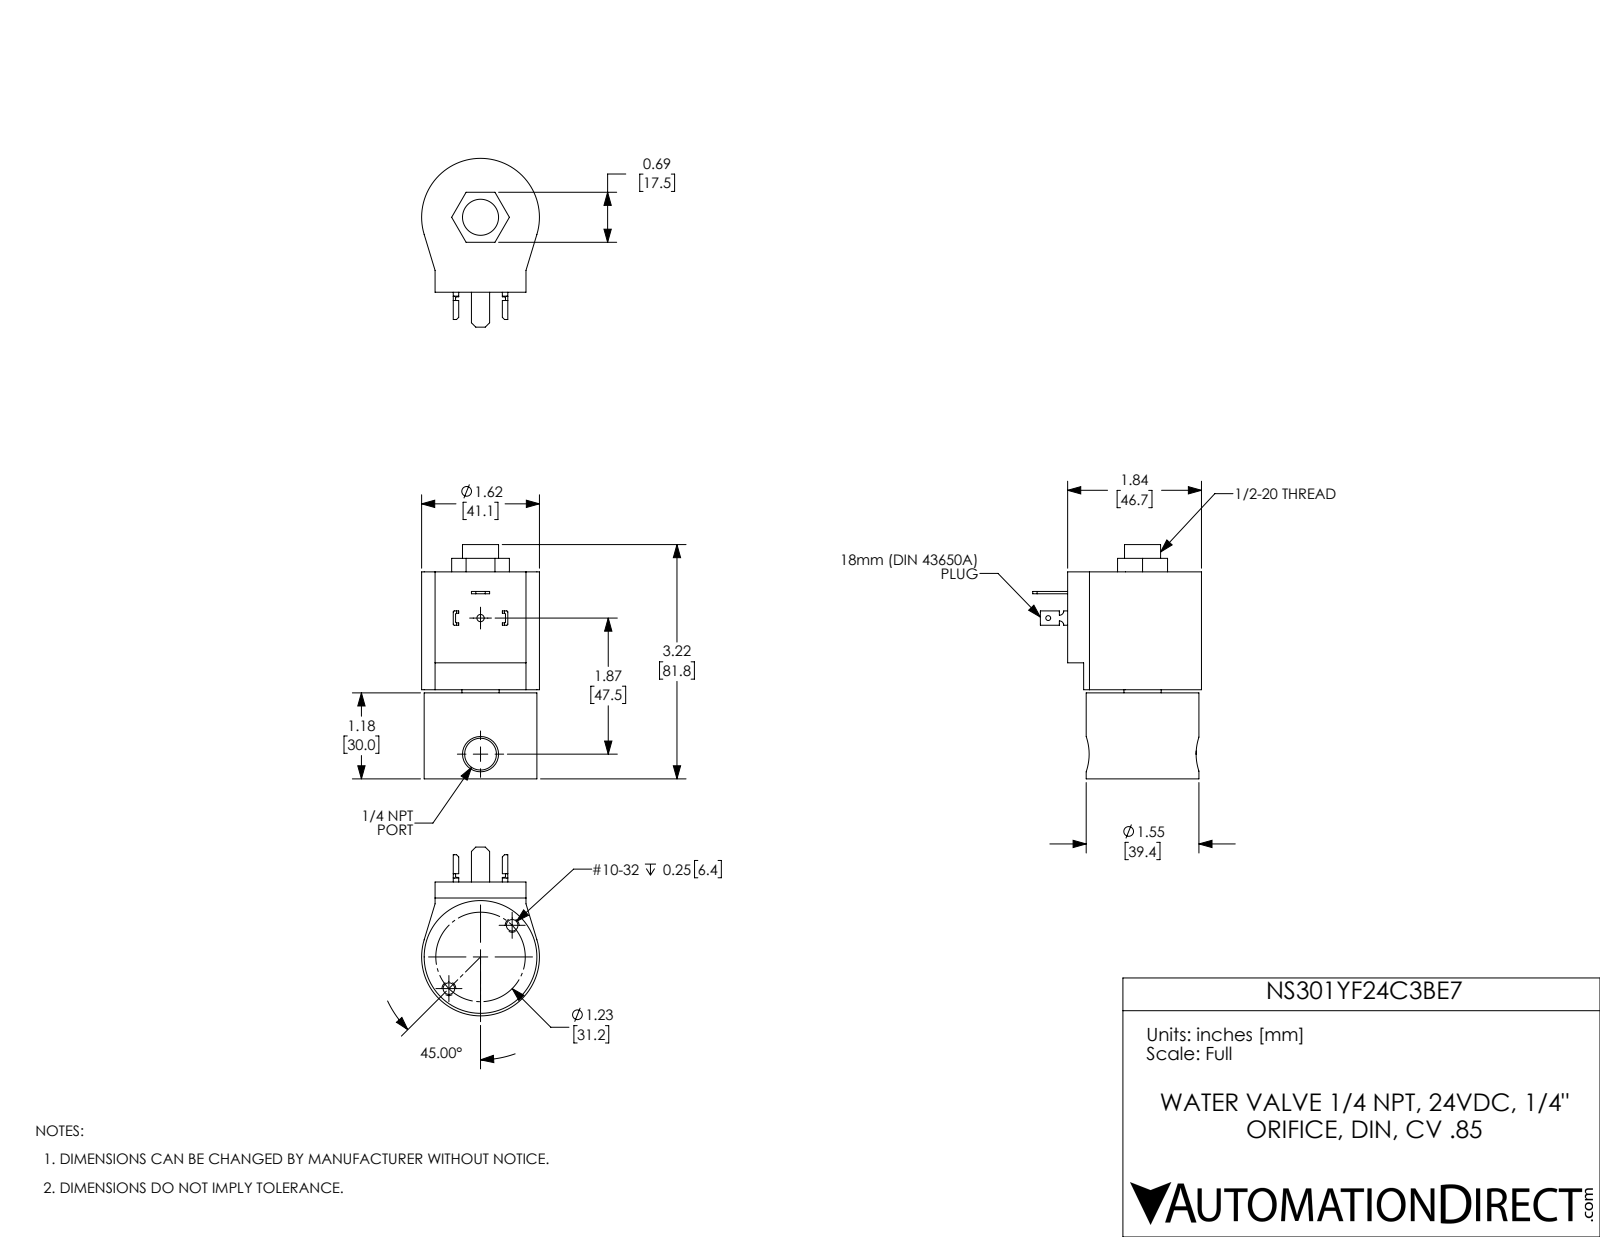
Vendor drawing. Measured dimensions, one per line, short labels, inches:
name: NS301YF16C3BE7
written by: SolidWorks 2017 (AUTOMOTIVE_DESIGN)
unit: in
bodies: 6 solids, 130 faces (73 planar, 49 cylindrical, 8 other)
size: 3.22 × 2.32 × 1.62
volume: 6.042 in³; area: 33.19 in²
holes: 2× ⌀0.159, 1× ⌀0.067, 1× ⌀0.1, 1× ⌀0.437, 1× ⌀0.496, 1× ⌀0.512, 1× ⌀1.155
bosses: 1× ⌀1.55
rounds: 8× R0.015, 2× R0.06, 1× R0.81
face distances: 2.845, 1.182, 1.663, 1.225, 0.043, 1.62, 1.287, 0.106, 0.062, 1.558
hole spacings: 0.615, 1.23, 1.87
